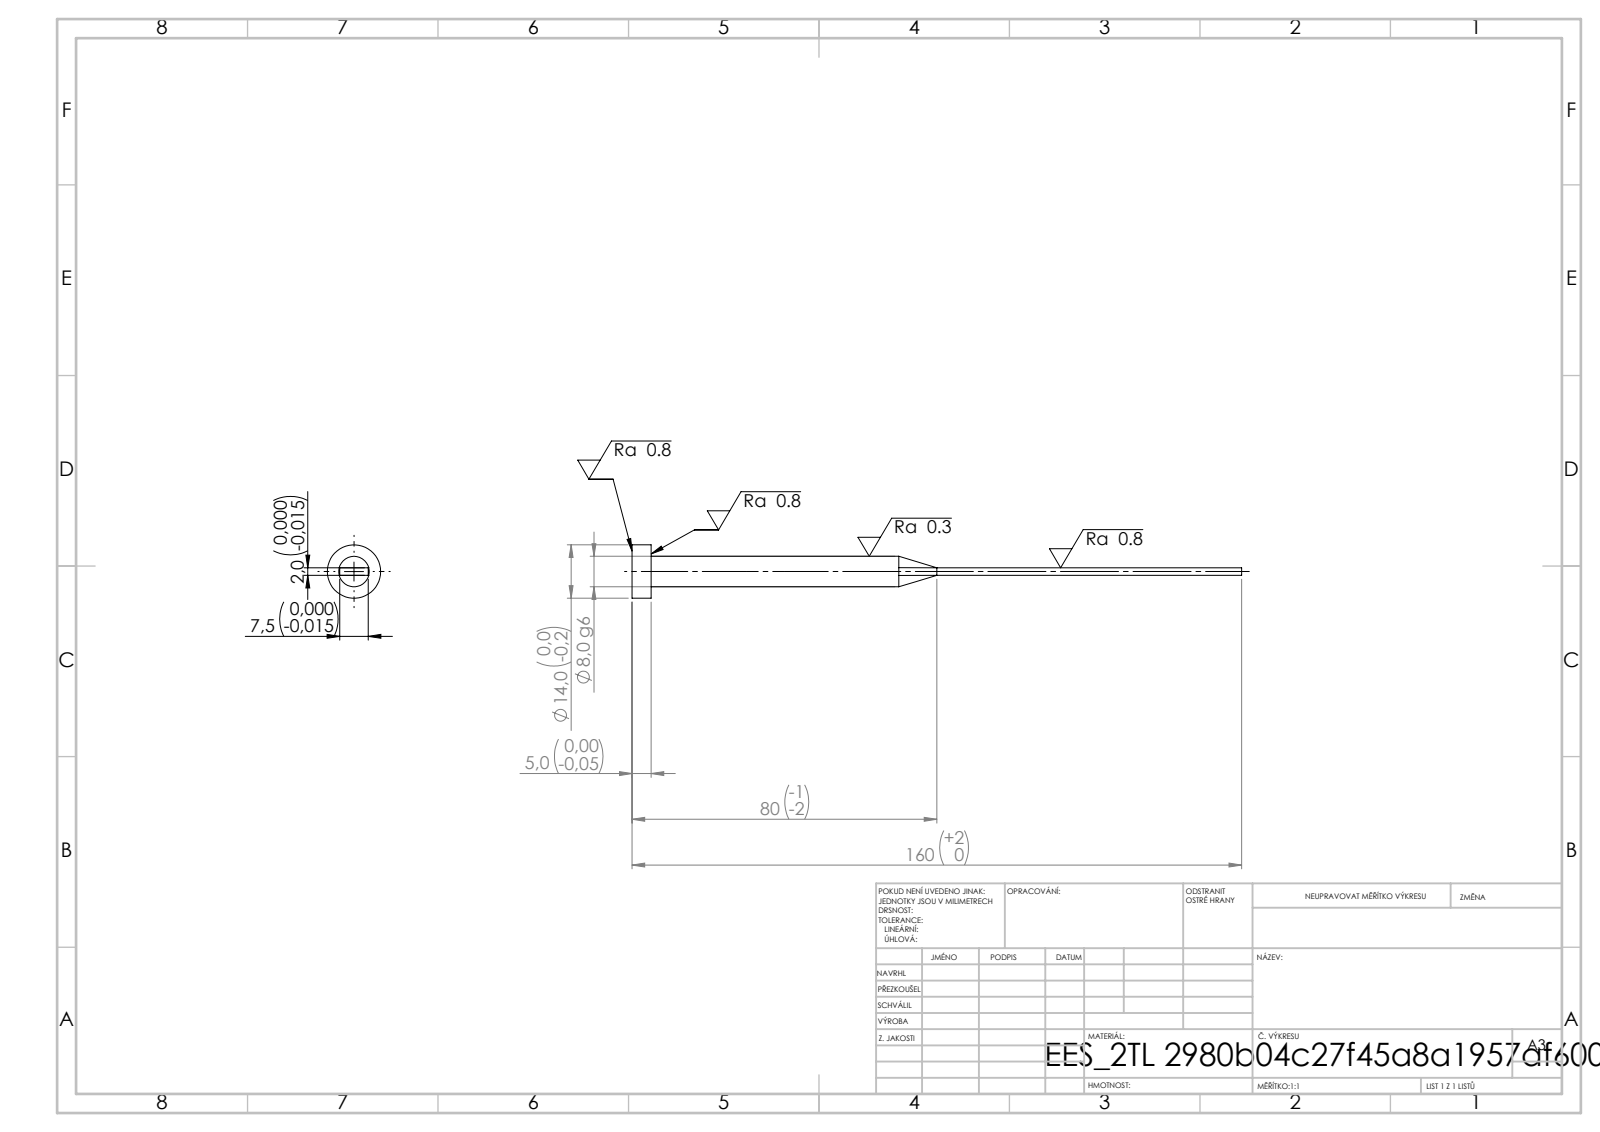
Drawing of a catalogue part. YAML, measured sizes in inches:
step_written_by: "SolidWorks 2019 (CONFIG_CONTROL_DESIGN)"
units: inches
bodies: {solids: 1, faces: 15, planar: 7, cylindrical: 4, other: 4}
overall_size: [6.299, 0.551, 0.551]
volume: 0.339
surface_area: 5.986
round_bosses_or_shafts:
  - {diameter: 0.551, count: 1}
  - {diameter: 0.315, count: 1}
face_to_face_distances: [0.079, 0.295, 0.197, 6.299, 6.102]
